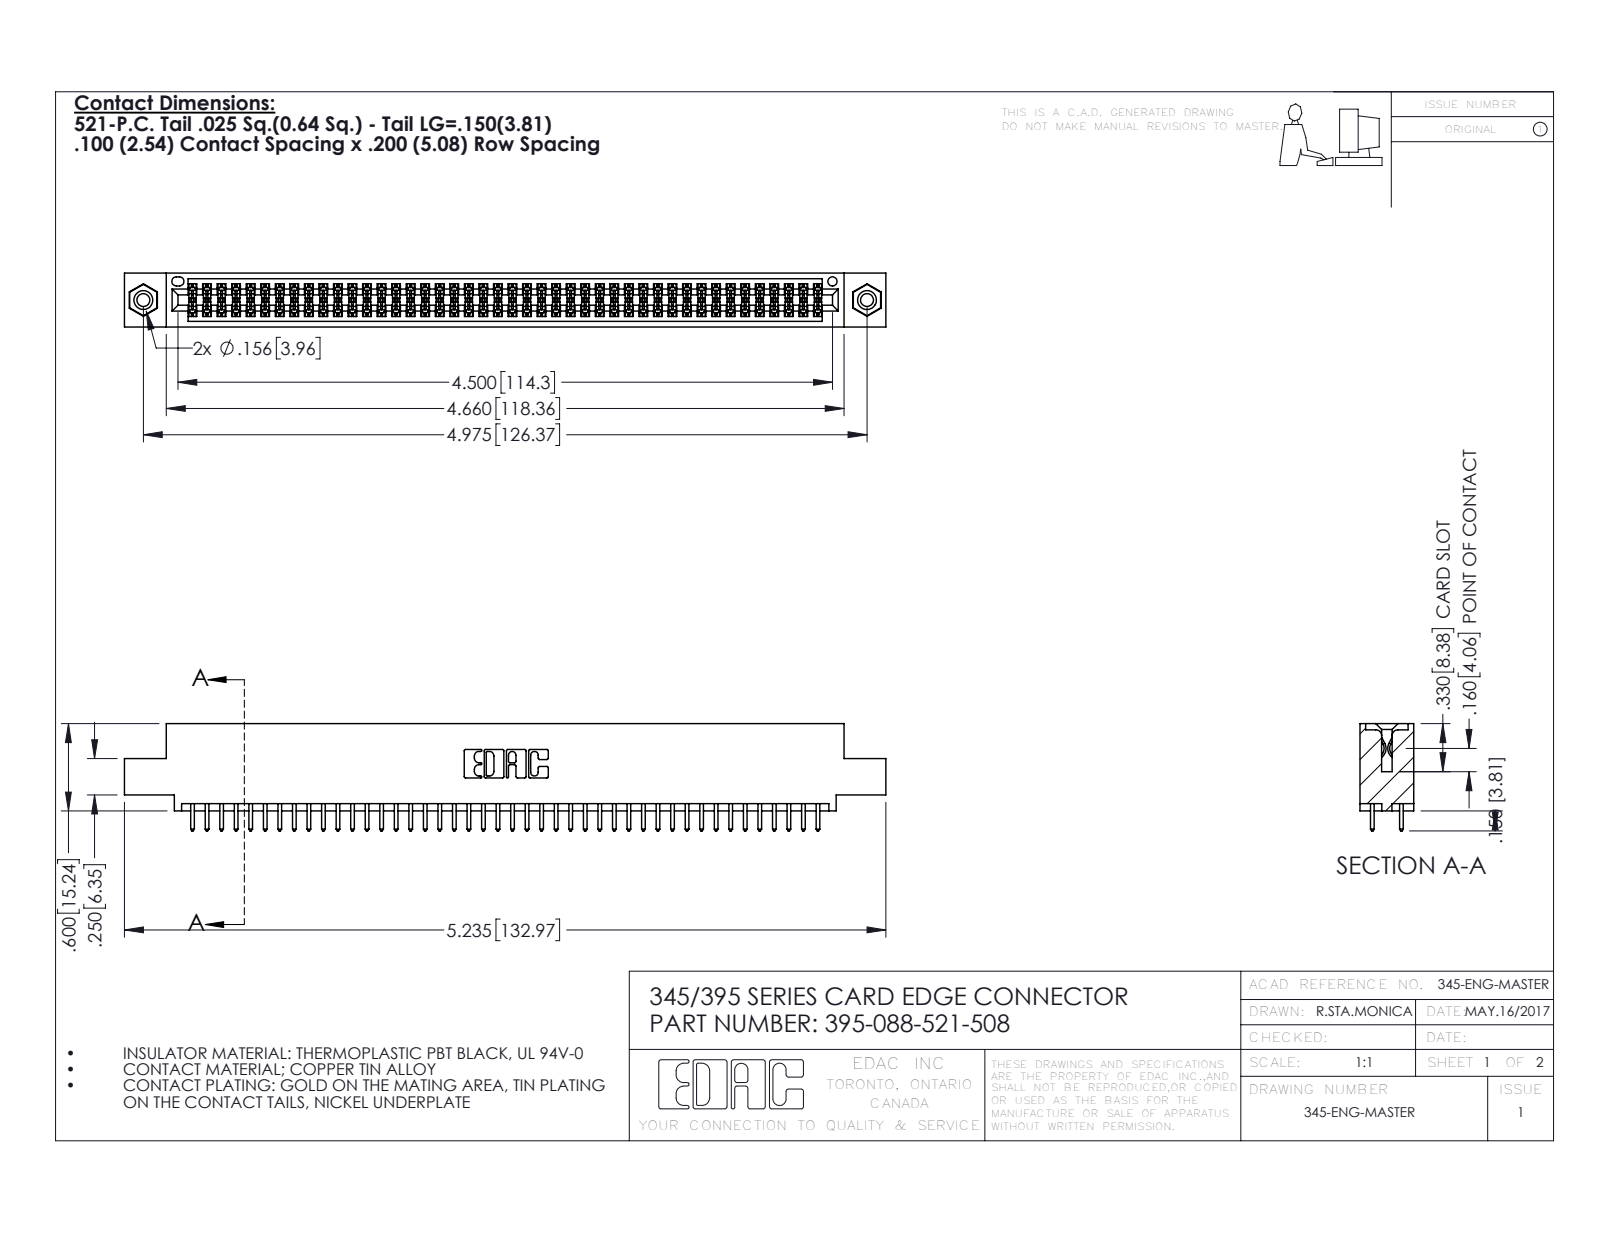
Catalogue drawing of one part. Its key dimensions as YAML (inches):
part_name: "395-088-521-508; 345-250-001_345-250-003-102; 345 Part_0.110 Offset - 0.156 Dia-TI; 345-292-001_345-293-121"
step_written_by: "SolidWorks 2016 (CONFIG_CONTROL_DESIGN)"
units: inches
bodies: {solids: 91, faces: 4590, planar: 3020, cylindrical: 1554, other: 16}
overall_size: [5.235, 0.737, 0.37]
volume: 0.782
surface_area: 29.23
round_holes:
  - {diameter: 0.089, count: 2}
  - {diameter: 0.125, count: 2}
  - {diameter: 0.156, count: 2}
  - {diameter: 0.064, count: 1}
round_bosses_or_shafts:
  - {diameter: 0.155, count: 2}
partial_cylinders:
  - {radius: 0.006, count: 132}
  - {radius: 0.01, count: 88}
  - {radius: 0.01, count: 22}
  - {radius: 0.007, count: 6}
  - {radius: 0.031, count: 6}
  - {radius: 0.026, count: 3}
  - {radius: 0.014, count: 2}
  - {radius: 0.019, count: 2}
face_to_face_distances: [0.072, 0.298, 0.2, 0.37, 0.098, 0.272, 0.025, 0.225, 0.175, 0.149]
hole_center_spacings: [0.27, 4.739, 4.975]
